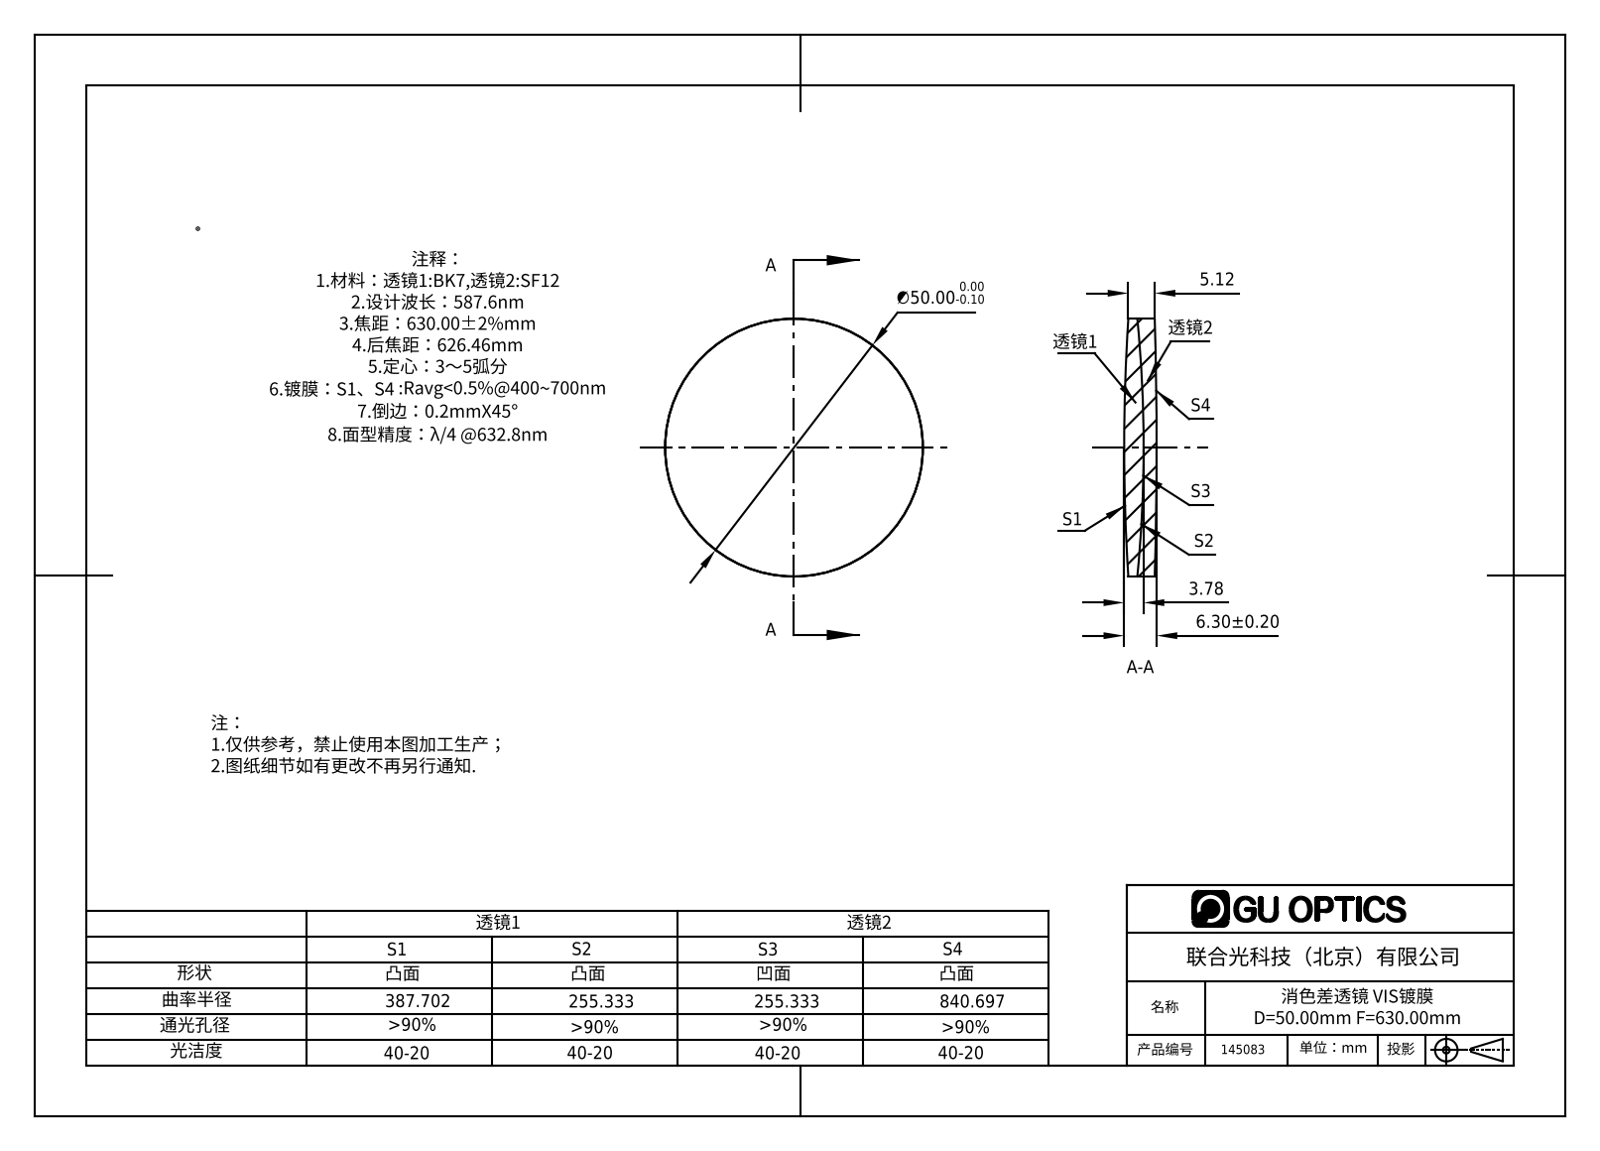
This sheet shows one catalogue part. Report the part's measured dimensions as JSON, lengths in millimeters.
{"part_name": "145083", "step_written_by": "SolidWorks 2016 (AUTOMOTIVE_DESIGN)", "units": "millimeters", "bodies": {"solids": 2, "faces": 12, "planar": 0, "cylindrical": 4, "other": 8}, "overall_size": [50, 50, 6.3], "volume_mm3": 11213, "surface_area_mm2": 8670, "round_bosses_or_shafts": [[50, 1]]}
